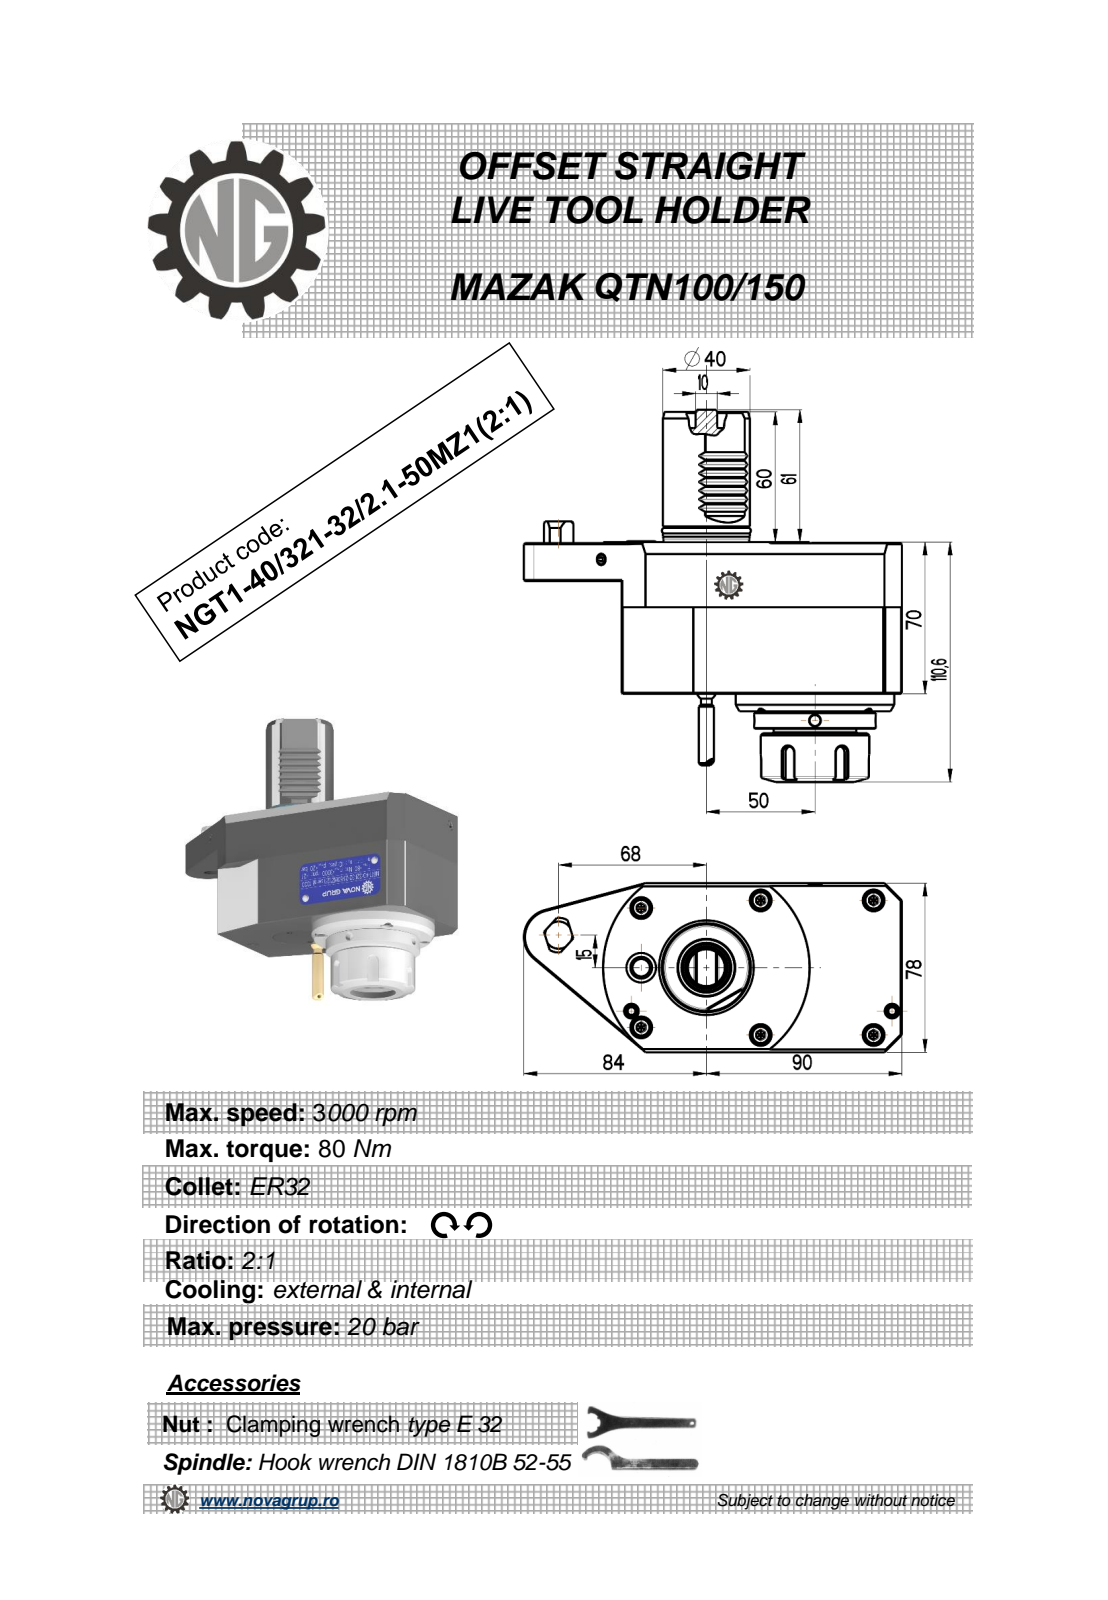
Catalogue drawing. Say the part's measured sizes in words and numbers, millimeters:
The part is named "NGT1_40_321_32_1_1_50MZ1". Its 3-D file was written by "PRO/ENGINEER BY PARAMETRIC TECHNOLOGY CORPORATION, 2010280 (CONFIG_CONTROL_DESIGN)". It is 1 solid with 271 faces: 110 planar, 69 cylindrical and 92 other. Overall it measures 174 by 171.6 by 78 millimeters. Its volume is 883 462 cubic millimeters and its surface area 73 936 square millimeters. Round holes: 2 of diameter 5, 1 of diameter 2.5, 1 of diameter 3, 1 of diameter 8, 1 of diameter 26, 1 of diameter 27. Round bosses or shafts: 1 of diameter 73, 1 of diameter 56, 1 of diameter 50, 1 of diameter 42, 1 of diameter 41, 1 of diameter 40, 1 of diameter 39.4, 1 of diameter 36.2. Partial cylindrical surfaces (rounded edges, fillets, slot ends): 7 of radius 0.3, 6 of radius 0.16, 5 of radius 3, 2 of radius 0.8, 1 of radius 8, 1 of radius 9, 1 of radius 12.97. The main face-to-face distances are 78, 70, 8, 129, 18, 60, 52, 7.5, 88.1, 8.5. The hole center spacings are 21.5, 30, 36.91, 50, 54.43, 80.
